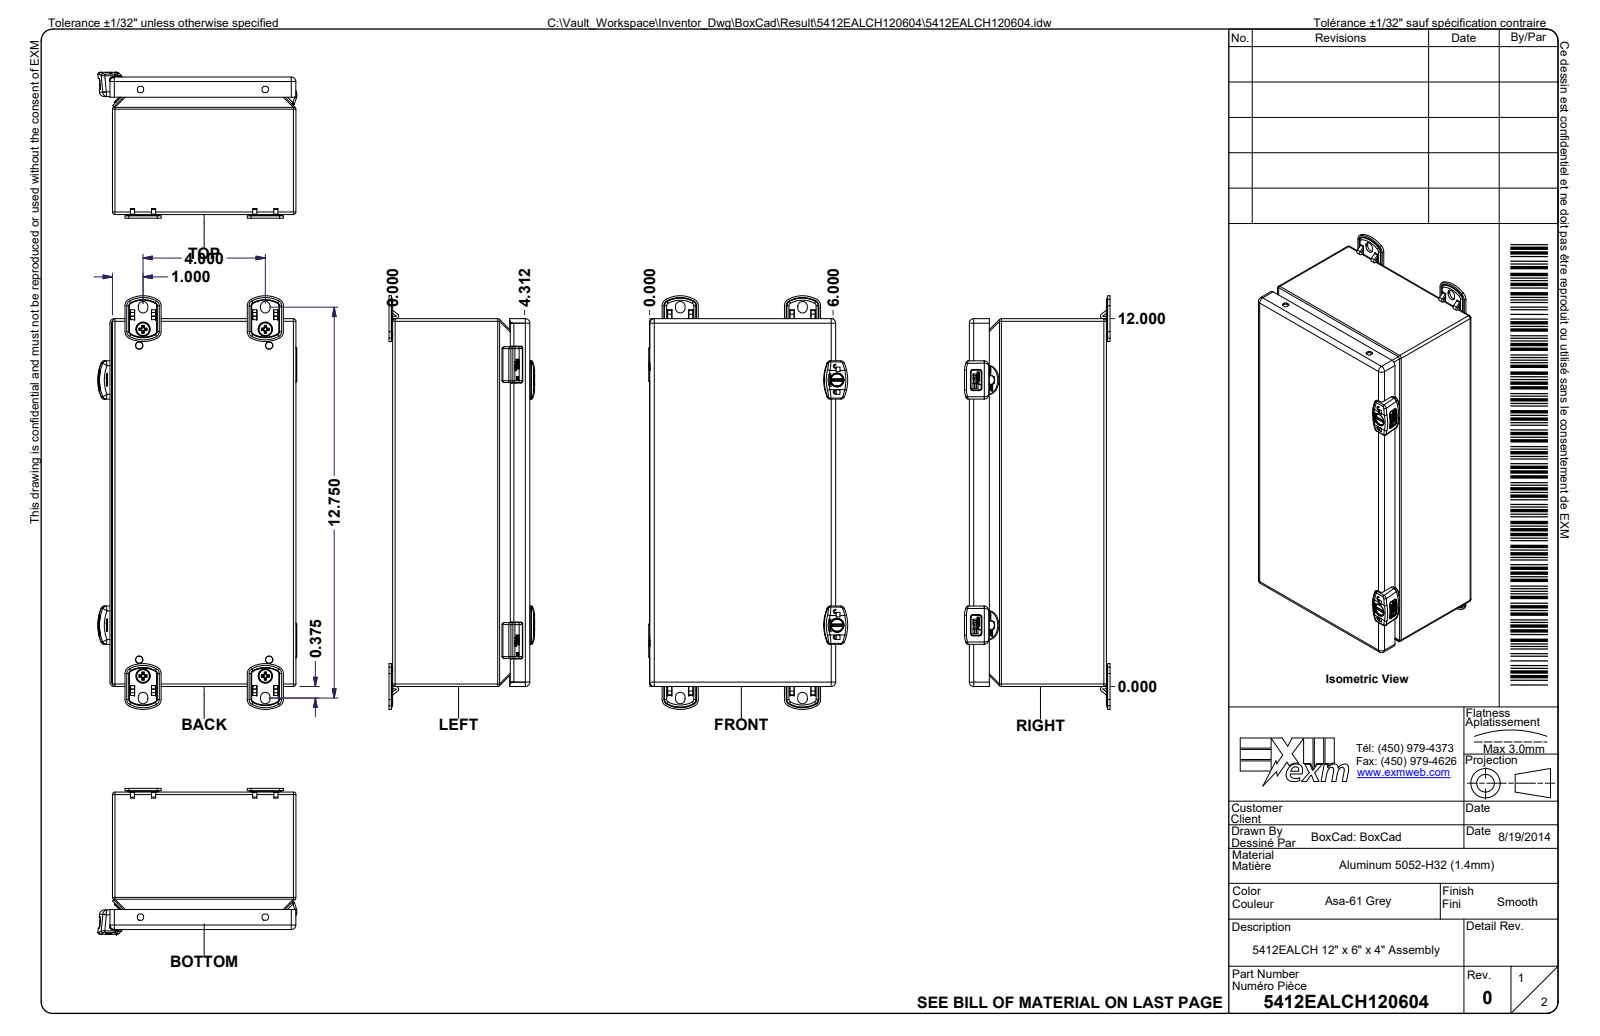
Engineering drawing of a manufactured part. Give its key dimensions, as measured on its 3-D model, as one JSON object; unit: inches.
{"part_name": "5412EALCH120604; 5412EALCH120604B; 5412EALCH120604B-P; STK-A-70469-1 (+8 more)", "step_written_by": "Autodesk Inventor 2020 (AUTOMOTIVE_DESIGN)", "units": "inches", "bodies": {"solids": 59, "faces": 8409, "planar": 3583, "cylindrical": 2002, "other": 2824}, "overall_size": [13.496, 6.503, 4.76], "volume_in3": 24.88, "surface_area_in2": 883, "round_holes": [[0.165, 4], [0.173, 4], [0.197, 4], [0.197, 4], [0.236, 4], [0.236, 4], [0.32, 4], [0.03, 2], [0.175, 2], [0.201, 2], [0.24, 2], [0.339, 2]], "round_bosses_or_shafts": [[0.232, 8], [0.5, 4], [0.3, 4], [0.236, 4], [0.193, 4], [0.197, 3], [0.412, 2], [0.394, 2]], "partial_cylinders_radius": [[0.02, 257], [0.01, 209], [0.039, 92], [0.004, 64], [0.008, 60], [0.059, 57], [0.031, 35], [0.005, 33]], "face_to_face_distances": [0.053, 0.053, 5.947, 4.433, 4.38, 4.486, 4.433, 0.236, 0.304, 4.196], "hole_center_spacings": [0.546, 4.159, 10.781, 11.543, 5.371, 1.507, 4.25, 4.25]}
